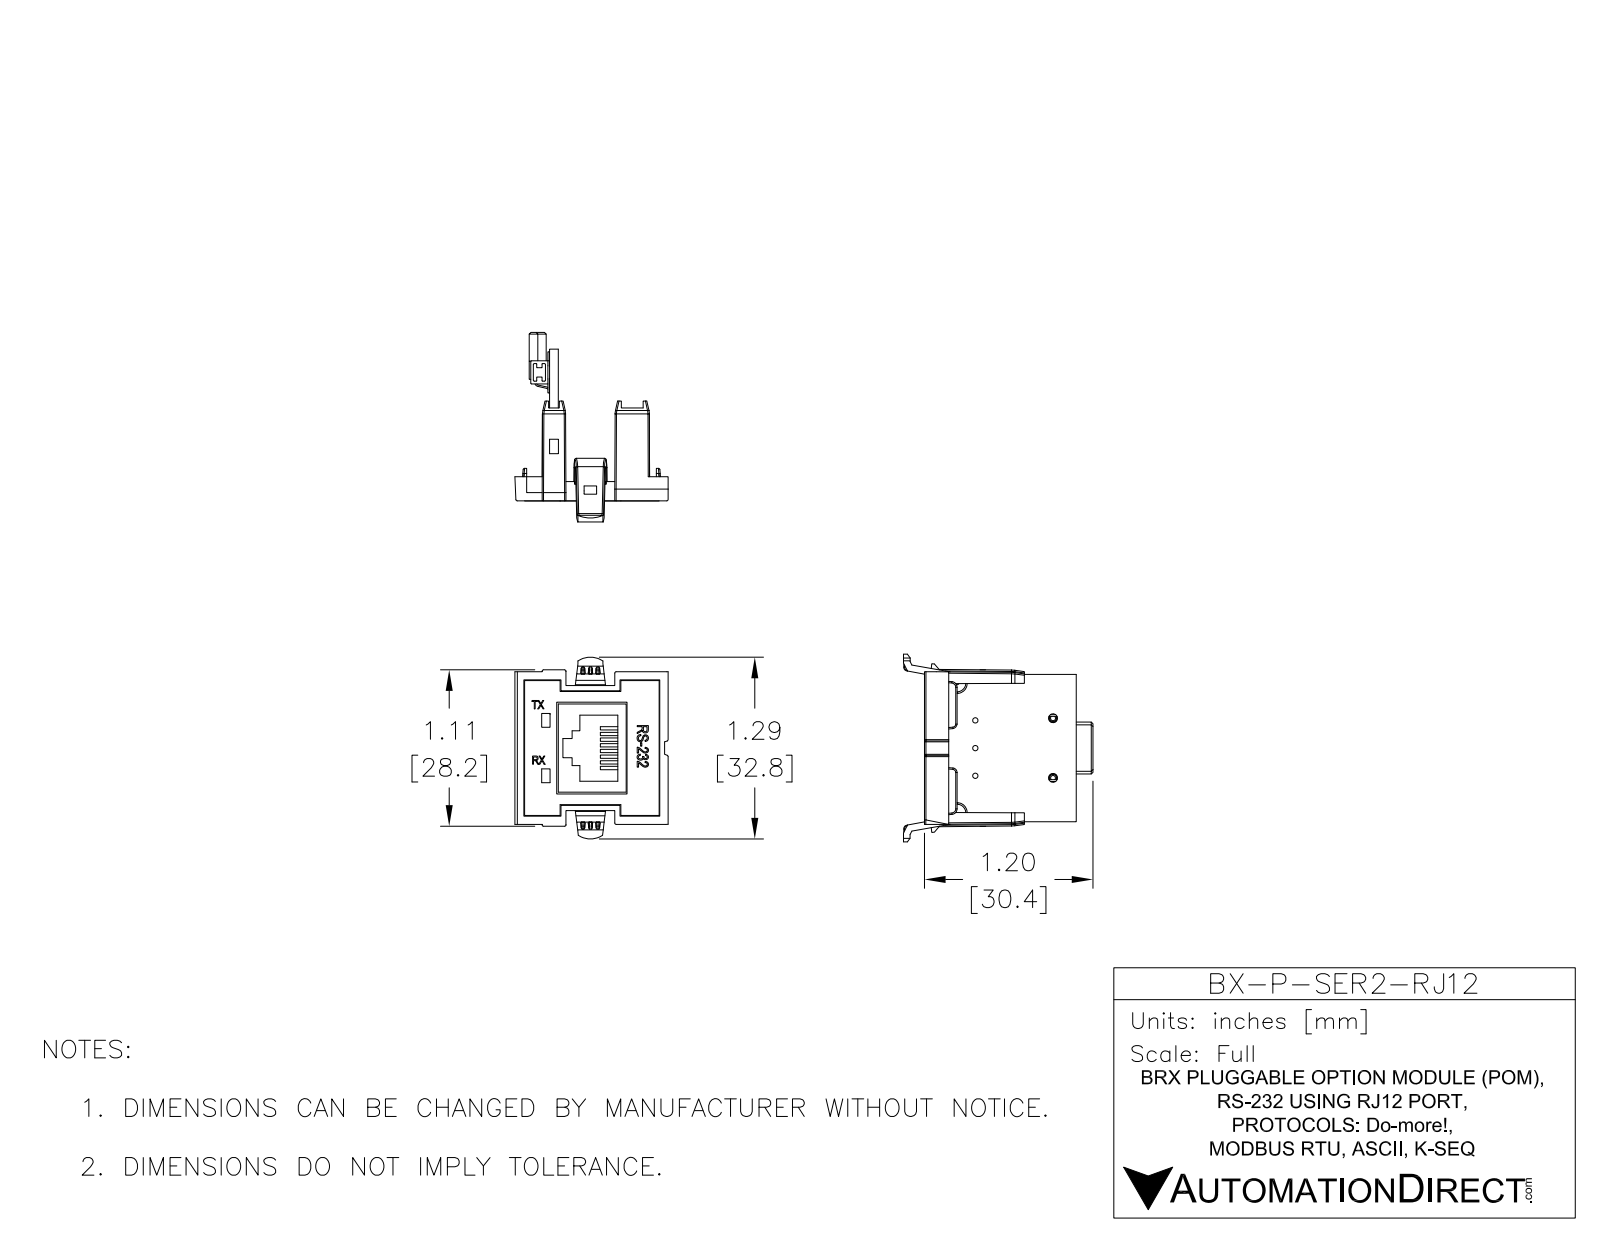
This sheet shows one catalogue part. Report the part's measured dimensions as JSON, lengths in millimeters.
{"part_name": "BX-P-SER2-RJ12", "step_written_by": "SolidWorks 2016 (AUTOMOTIVE_DESIGN)", "units": "millimeters", "bodies": {"solids": 45, "faces": 1929, "planar": 1598, "cylindrical": 271, "other": 60}, "overall_size": [33.9, 33.88, 27.53], "volume_mm3": 4782, "surface_area_mm2": 8566, "round_holes": [[0.95, 3], [1.6, 2]], "partial_cylinders_radius": [[0.2, 47], [0.1, 40], [0.85, 10], [0.14, 8], [0.41, 5], [1.25, 5], [0.13, 4], [0.23, 4]], "face_to_face_distances": [1.58, 1.27, 1.68, 13.21, 0.5, 1.57, 1.67, 10.4, 11.67, 21.5], "hole_center_spacings": [14.03, 4.99, 5, 9.99, 10.77, 15.02, 15.03, 17.44]}
